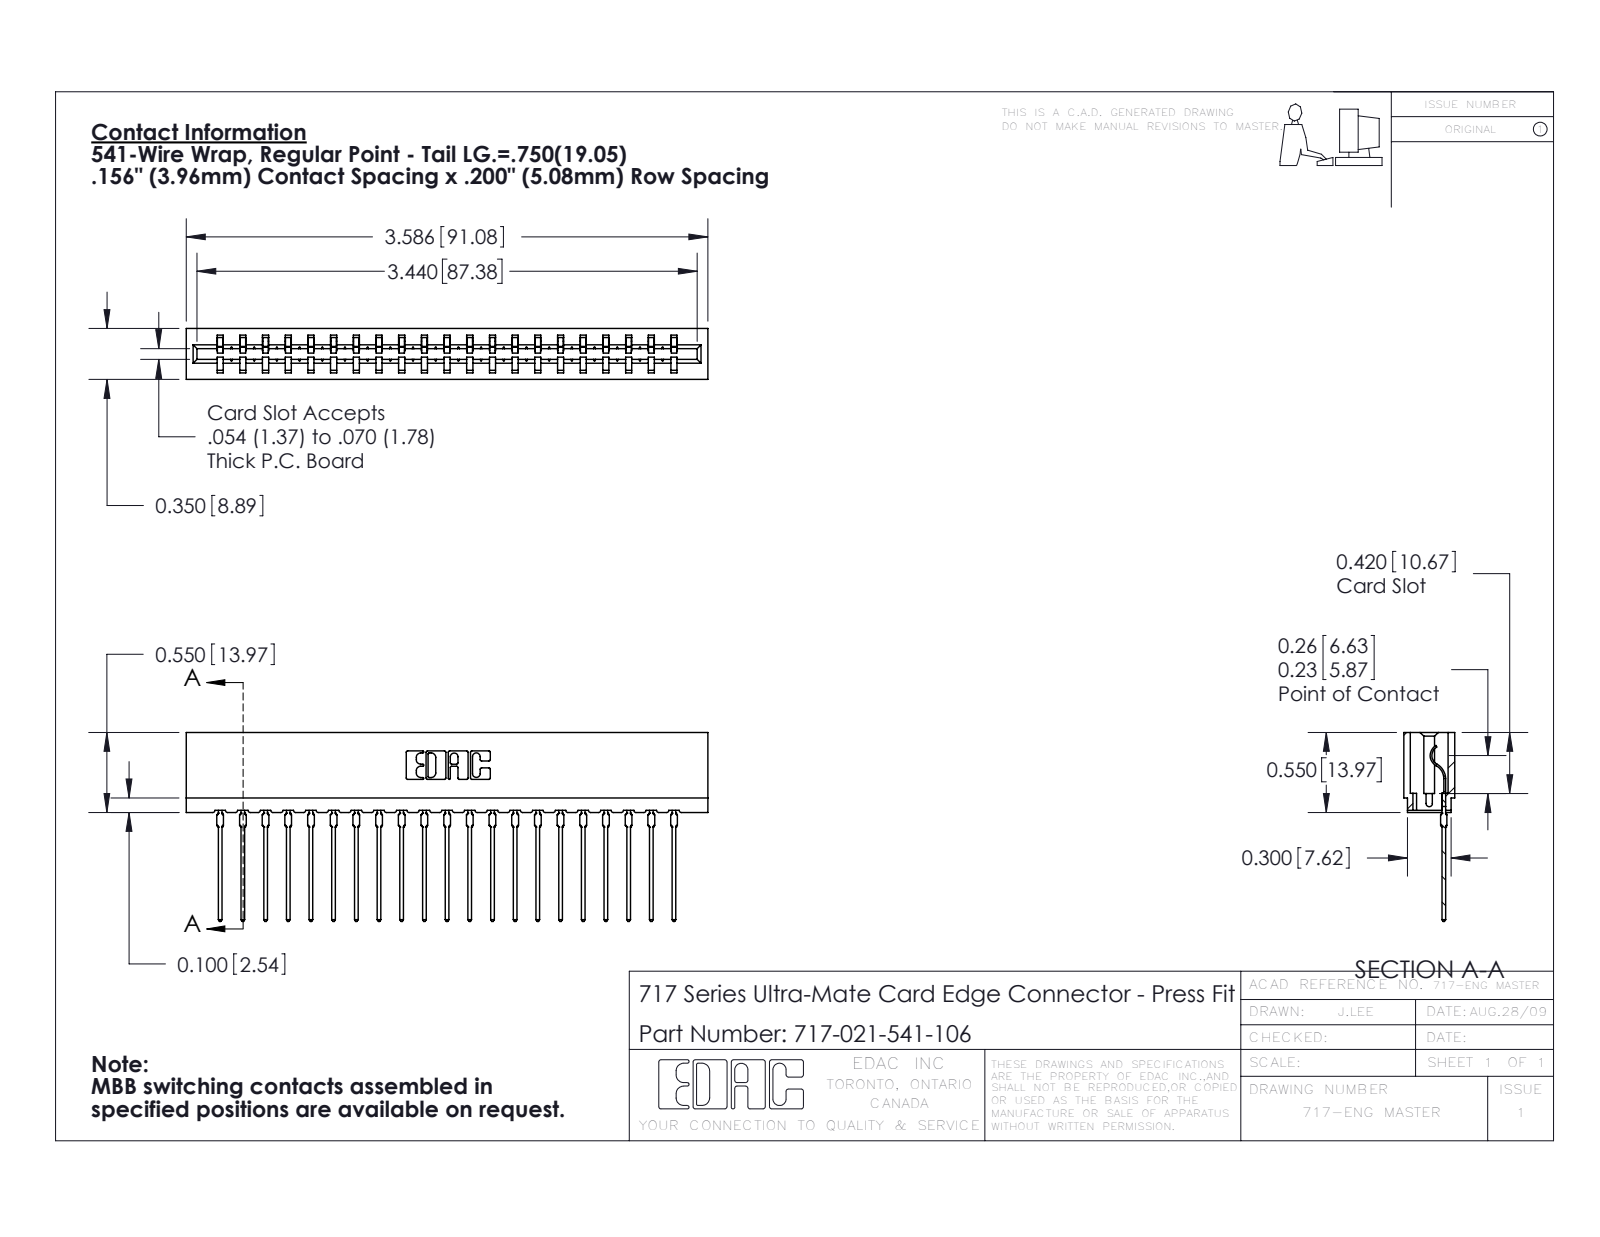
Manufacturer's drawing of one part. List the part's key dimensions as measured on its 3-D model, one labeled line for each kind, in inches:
Part name (STEP PRODUCT): 717-021-541-106; 745-292-001_541; 717 Part_Insulator Option - 06
STEP written by: SolidWorks 2016 (CONFIG_CONTROL_DESIGN)
Units: inches
Bodies: 22 solids, 2467 faces (1482 planar, 439 cylindrical, 546 other)
Overall size (bounding box): 3.586 × 1.299 × 0.35
Volume: 0.481 in³ · Surface area: 17.48 in²
Partial cylindrical surfaces — rounded edges, fillets, slot ends (radius × count): R0.015 ×42, R0.021 ×42, R0.01 ×22, R0.007 ×6, R0.031 ×6, R0.005 ×4, R0.011 ×4, R0.026 ×3
Main face-to-face distances: 0.212, 0.138, 0.35, 0.156, 0.624, 0.063, 0.287, 0.076, 0.149, 0.074
